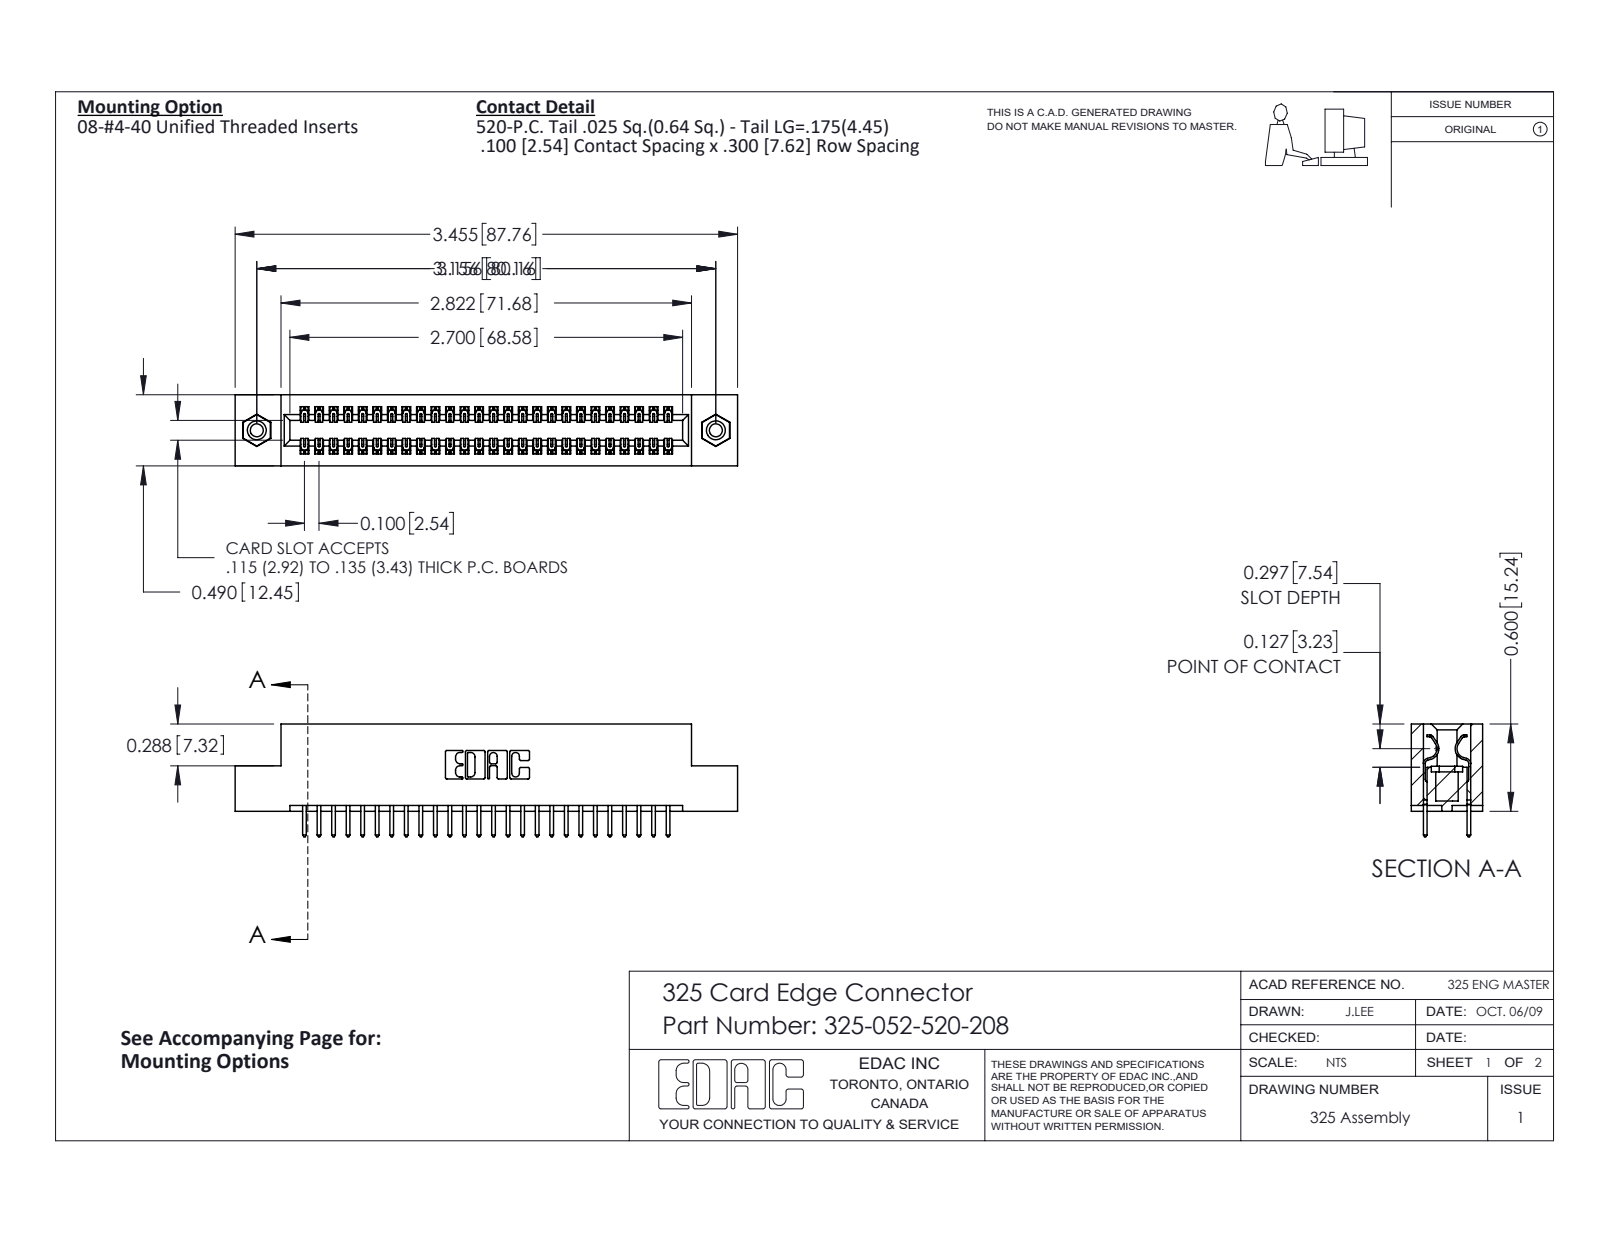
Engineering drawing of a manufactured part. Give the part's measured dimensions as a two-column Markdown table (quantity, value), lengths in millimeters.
| quantity | value |
| --- | --- |
| part name | 325-052-520-208; 325-292-001_325-293-120; 345-250-001_345-250-003-102; 325 Part_TI |
| STEP written by | SolidWorks 2016 (CONFIG_CONTROL_DESIGN) |
| units | millimeters |
| bodies | 55 solids, 2878 faces (1974 planar, 888 cylindrical, 16 other) |
| overall size | 87.8 × 19.7 × 12.4 |
| volume | 11 200 mm³ |
| surface area | 13 050 mm² |
| round holes (diameter × count) | 2.3 × 2, 3.2 × 2, 4.1 × 2 |
| round bosses / shafts (diameter × count) | 3.9 × 2 |
| partial cylindrical surfaces (radius × count) | 0.2 × 78, 0.3 × 52, 0.3 × 22, 0.2 × 6, 0.8 × 6, 0.7 × 3, 0.4 × 2, 0.6 × 2 |
| main face-to-face distances | 2.1, 10.3, 7.6, 12.4, 2.7, 9.7, 0.6, 8.3, 1, 7 |
| hole center spacings | 80.2 |
